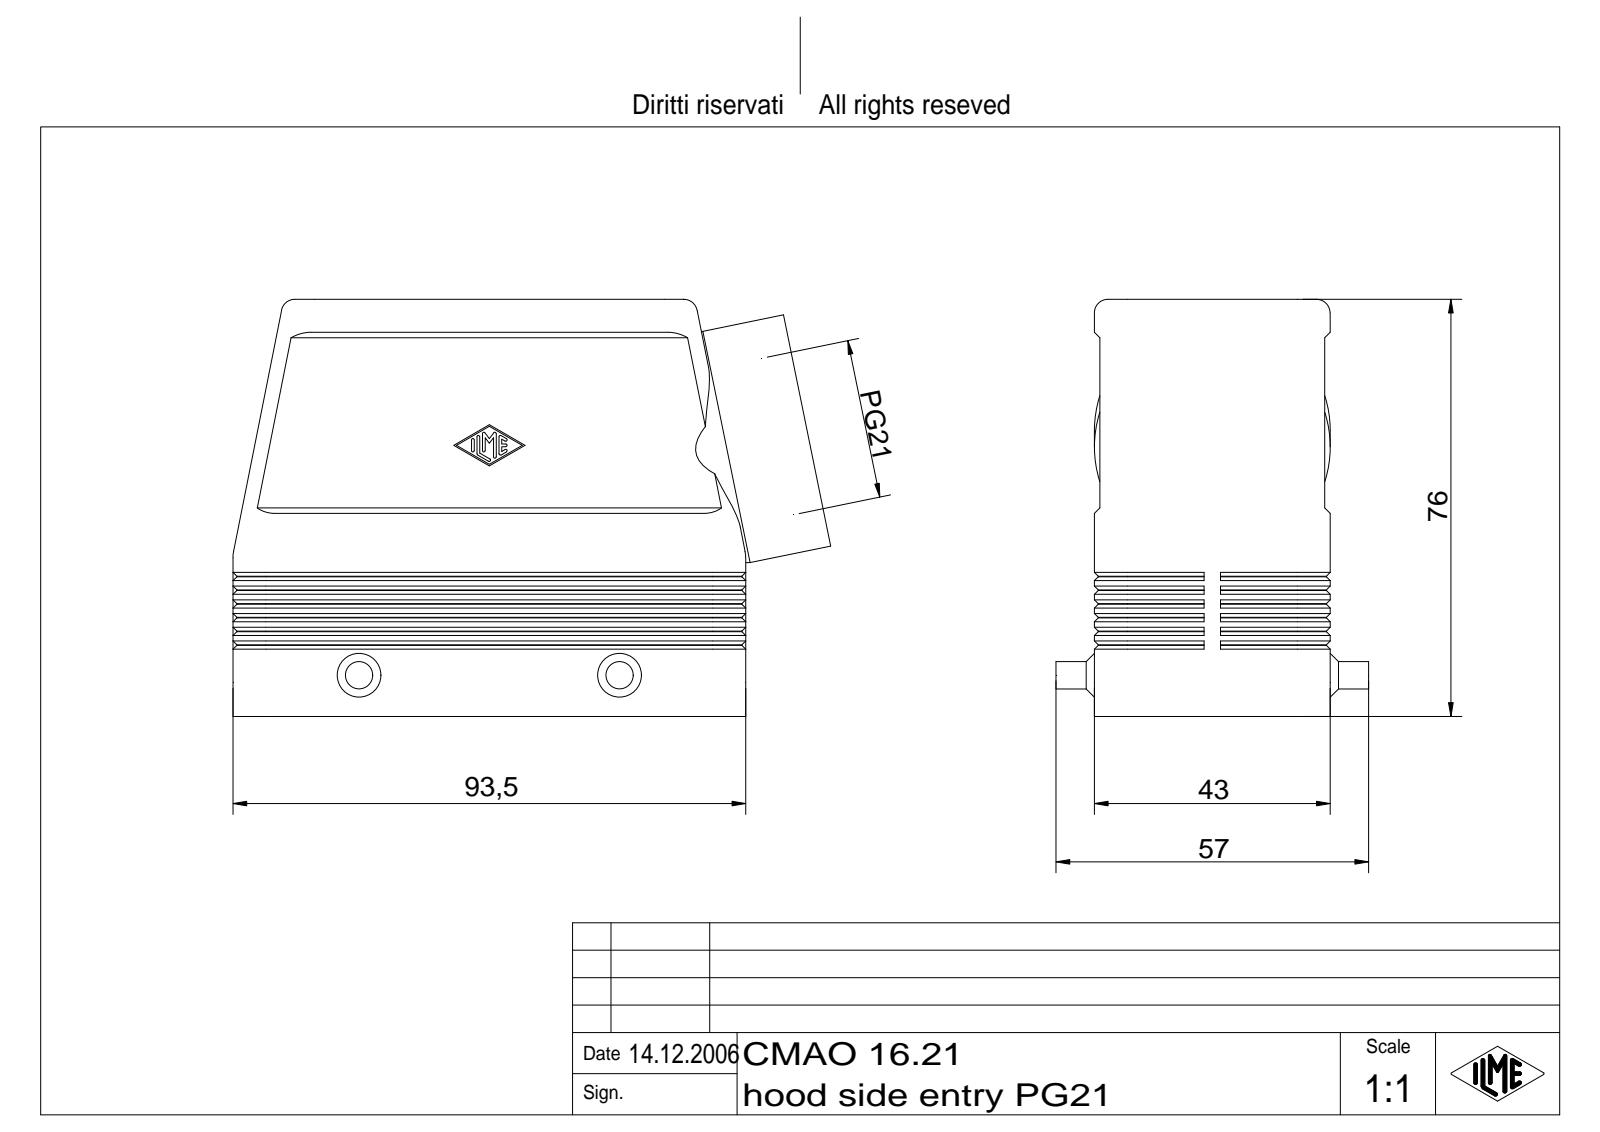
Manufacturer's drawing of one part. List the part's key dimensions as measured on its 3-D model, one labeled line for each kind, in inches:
Part name (STEP PRODUCT): CAO Tüllengehäuse 2 Bügel für einen Einsatz
STEP written by: Autodesk Inventor 7 (AUTOMOTIVE_DESIGN)
Units: inches
Bodies: 1 solid, 526 faces (192 planar, 134 cylindrical, 200 other)
Overall size (bounding box): 4.291 × 2.992 × 2.244
Volume: 5.211 in³ · Surface area: 73.64 in²
Round holes (diameter × count): ⌀0.976 ×1, ⌀1.054 ×1
Round bosses / shafts (diameter × count): ⌀0.197 ×2, ⌀1.693 ×1
Partial cylindrical surfaces — rounded edges, fillets, slot ends (radius × count): R0.01 ×14, R0.236 ×10, R0.079 ×4, R0.098 ×4, R0.118 ×4, R0.209 ×2
Main face-to-face distances: 0.118, 1.457, 0.079, 1.535, 0.039, 1.654, 1.575, 1.614, 1.693, 0.07
